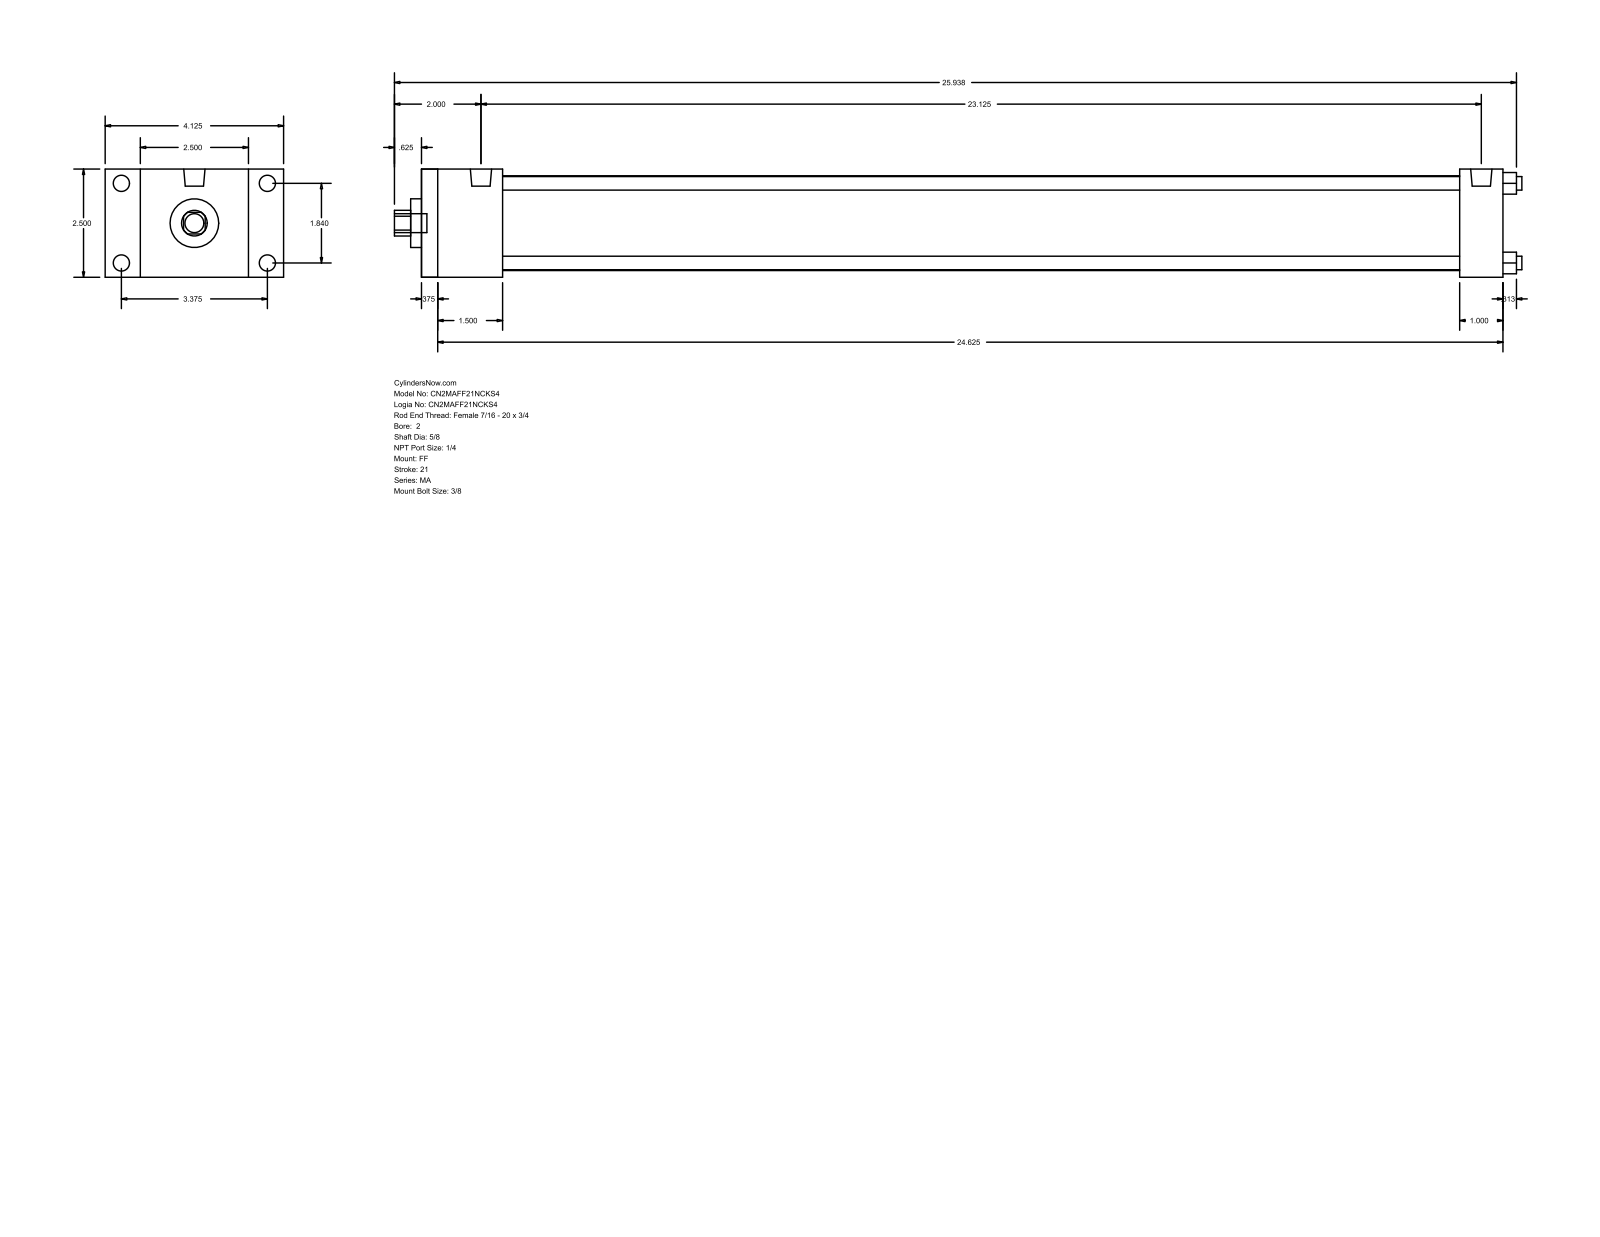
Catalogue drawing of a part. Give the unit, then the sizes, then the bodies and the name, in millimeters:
Units: millimetres
Overall size (bounding box): 661.99 × 104.78 × 63.5
Round holes (diameter × count): ⌀7.94 ×4, ⌀15.88 ×1, ⌀28.57 ×1, ⌀55.63 ×1
Round bosses / shafts (diameter × count): ⌀9.53 ×4, ⌀7.94 ×4, ⌀12.49 ×2, ⌀11.11 ×1
Partial cylindrical surfaces — rounded edges, fillets, slot ends (radius × count): R7.54 ×1
Main face-to-face distances: 63.5, 635, 9.52, 625.48, 25.4, 38.1, 47.62, 609.6, 600.08, 561.98
Hole centre spacings: 33.05, 46.74, 66.1
Bodies: 0 solids, 92 faces (64 planar, 28 cylindrical, 0 other)
Part name (STEP PRODUCT): MA_FF__0200_0.625
STEP written by: GSSL Pune (CONFIG_CONTROL_DESIGN)
